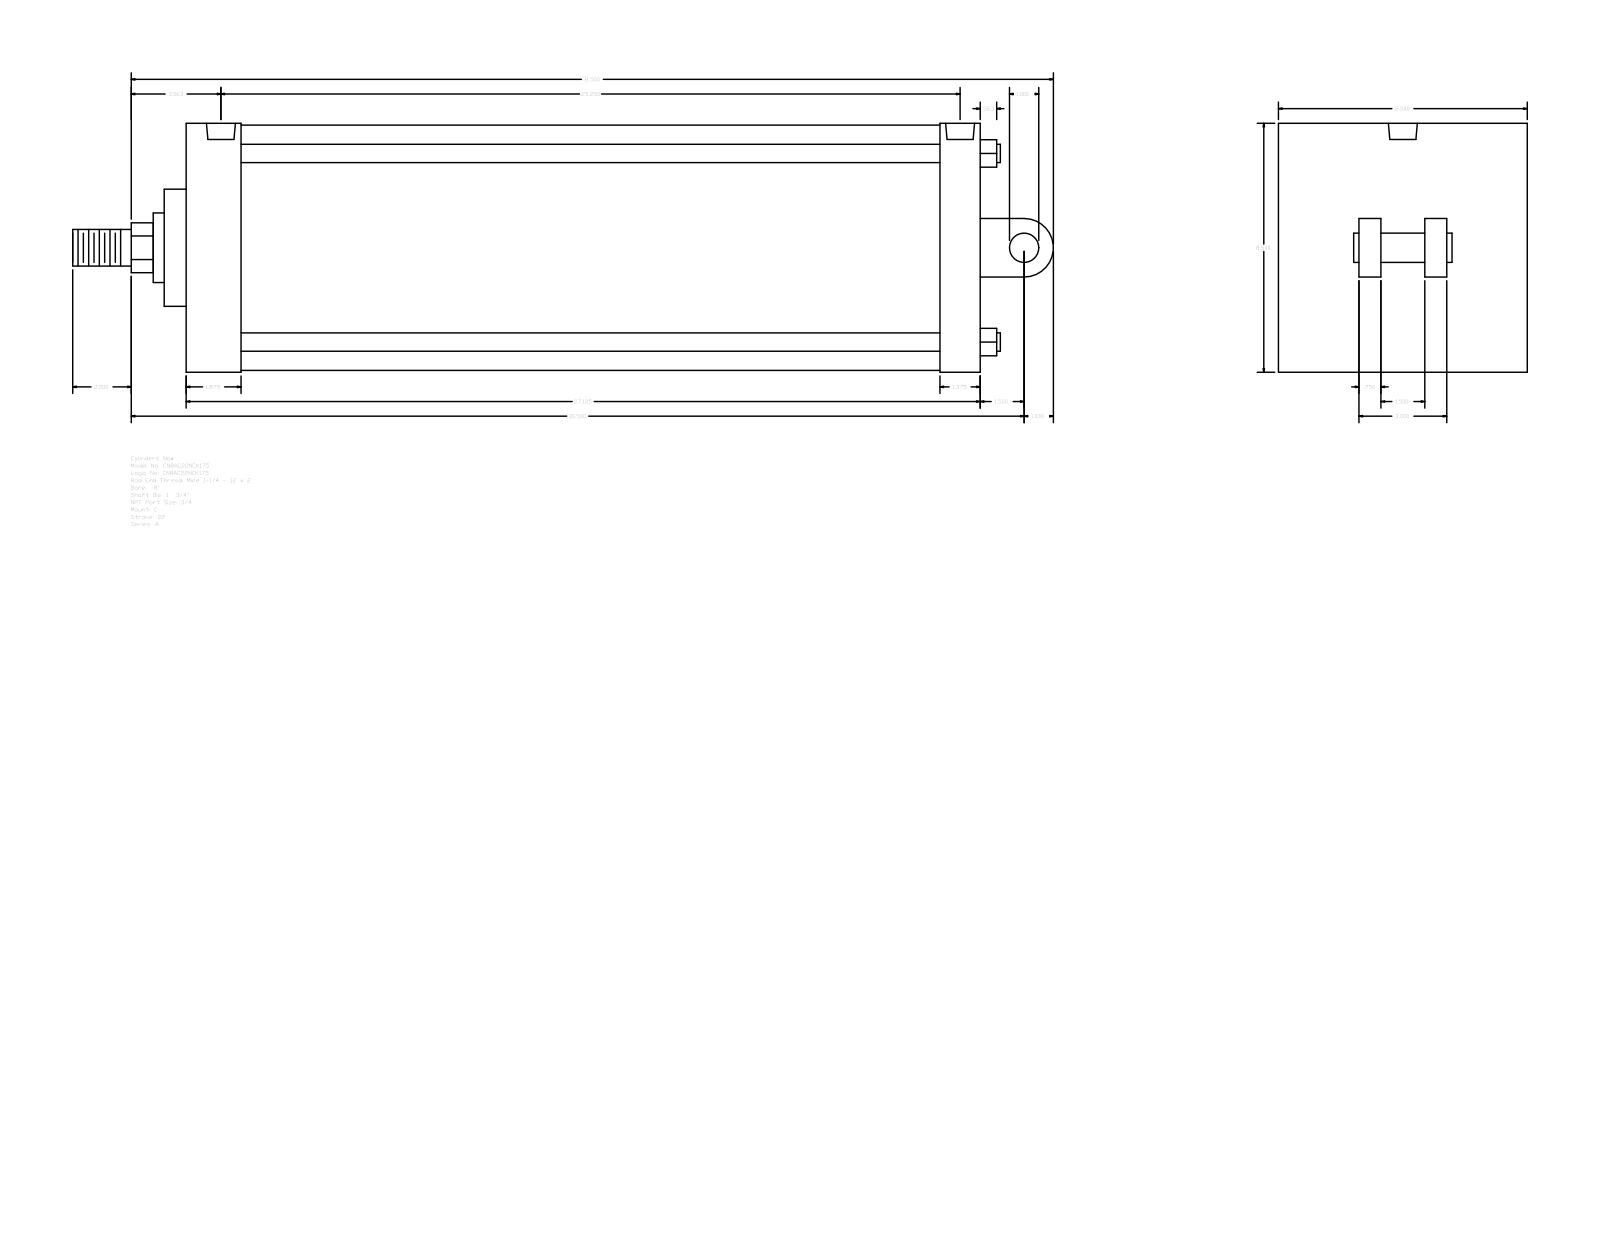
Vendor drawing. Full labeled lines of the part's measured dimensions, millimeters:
Part name (STEP PRODUCT): A_C__0800_1.75
STEP written by: GSSL Pune (CONFIG_CONTROL_DESIGN)
Units: millimetres
Bodies: 0 solids, 104 faces (75 planar, 29 cylindrical, 0 other)
Overall size (bounding box): 850.9 × 215.9 × 215.9
Round holes (diameter × count): ⌀15.08 ×4, ⌀25.12 ×2
Round bosses / shafts (diameter × count): ⌀15.88 ×4, ⌀212.72 ×1, ⌀60.33 ×1, ⌀44.45 ×1, ⌀31.75 ×1, ⌀25.4 ×1
Partial cylindrical surfaces — rounded edges, fillets, slot ends (radius × count): R21.63 ×1, R25.4 ×1
Main face-to-face distances: 688.98, 215.9, 19.05, 57.15, 47.63, 641.35, 654.05, 606.42, 34.93, 69.85
Hole centre spacings: 6.35, 628.65, 635, 641.35
